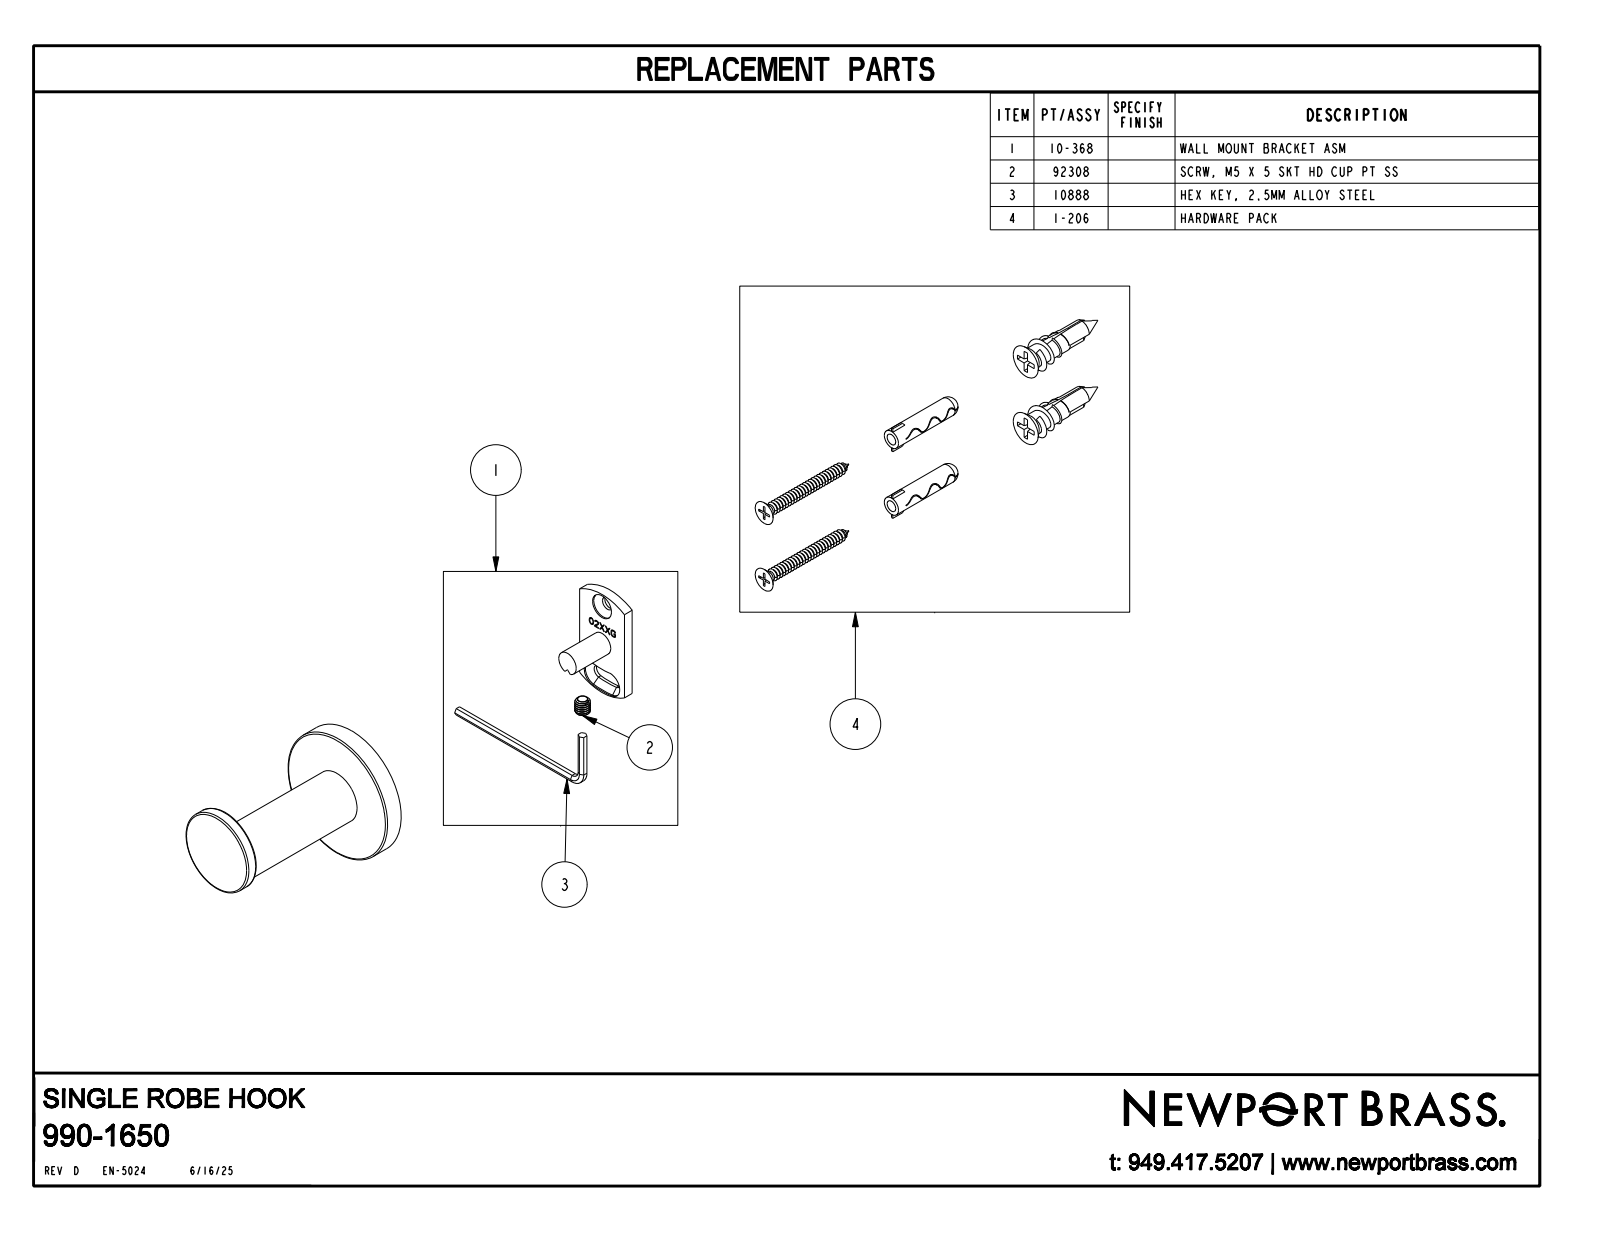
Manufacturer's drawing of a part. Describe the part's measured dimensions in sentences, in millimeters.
The part is named "990-1650". Its 3-D file was written by "CREO PARAMETRIC BY PTC INC, 2018400 (CONFIG_CONTROL_DESIGN)". It is 1 solid with 17 faces: 5 planar, 6 cylindrical and 6 other. Overall it measures 60.7 by 44.5 by 44.5 millimeters. Its volume is 25 470 cubic millimeters and its surface area 7 871 square millimeters. Round bosses or shafts: 1 of diameter 44.5, 1 of diameter 28, 1 of diameter 18. The main face-to-face distances are 6.6, 60.7, 54.1, 56.6, 50, 4.1.
